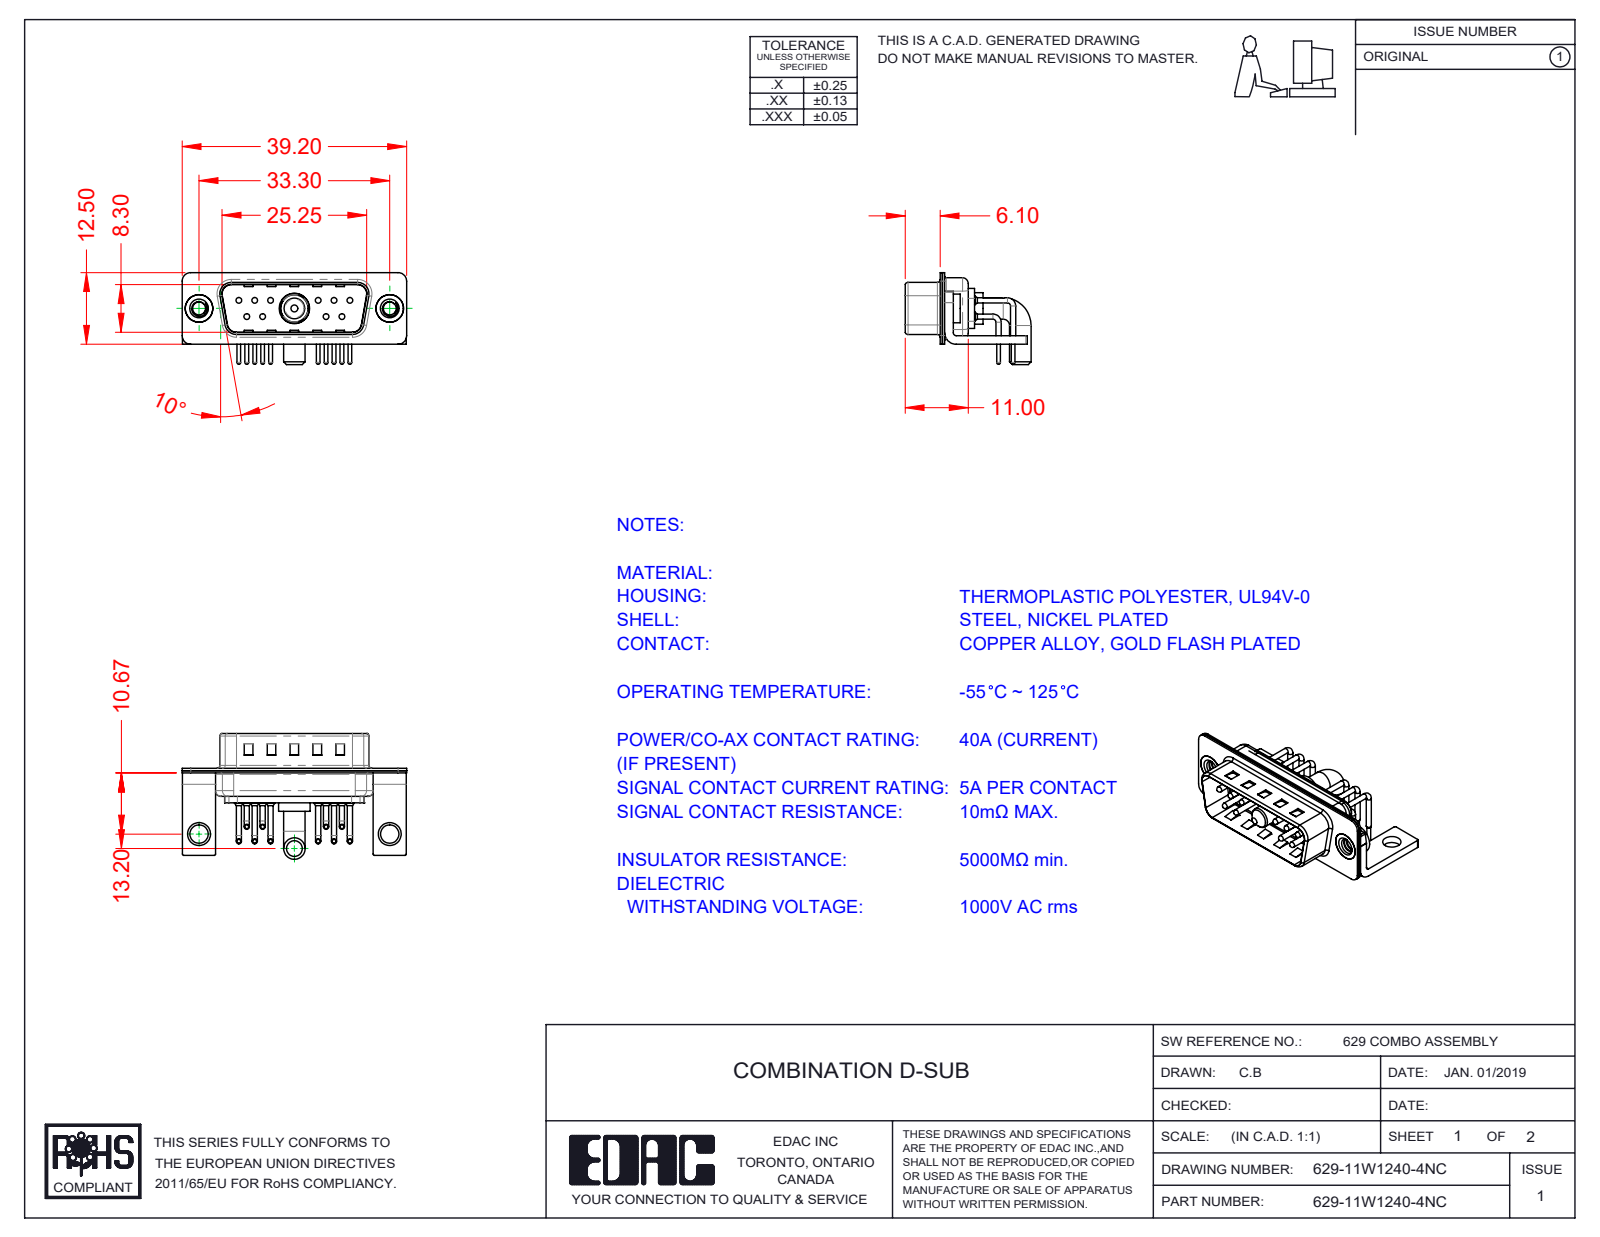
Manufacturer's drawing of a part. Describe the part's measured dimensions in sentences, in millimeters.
The part is named "629Combo Contact Row 2; 629Combo Threaded Rivet_2; 629Combo Housing_11W1; 629Combo Stabilizer Bracket (+5 more)". Its 3-D file was written by "SolidWorks 2020 (CONFIG_CONTROL_DESIGN)". It is 19 solids with 1544 faces: 818 planar, 542 cylindrical and 184 other. Overall it measures 39.2 by 21.98 by 16.05 millimeters. Its volume is 2 448 cubic millimeters and its surface area 5 920 square millimeters. Round holes: 10 of diameter 0.75, 10 of diameter 1.6, 10 of diameter 2, 2 of diameter 2.26, 2 of diameter 3.2, 2 of diameter 4, 2 of diameter 4.8, 1 of diameter 4.85, 1 of diameter 5.3. Round bosses or shafts: 20 of diameter 0.9, 10 of diameter 1.5, 10 of diameter 1, 10 of diameter 0.65, 2 of diameter 5, 2 of diameter 4.9, 2 of diameter 3.75, 1 of diameter 5.5. Partial cylindrical surfaces (rounded edges, fillets, slot ends): 16 of radius 0.25, 16 of radius 1.5, 13 of radius 2, 10 of radius 1.01, 9 of radius 0.5, 8 of radius 1.6, 7 of radius 1, 4 of radius 0.6. The main face-to-face distances are 0.4, 0.8, 1.5, 9.5, 9.1, 0.6, 8.7, 9.9, 1.2, 2.1. The hole center spacings are 3.16, 2.77, 13.85, 11.08, 16.62, 5.03, 5.04, 5.54.
